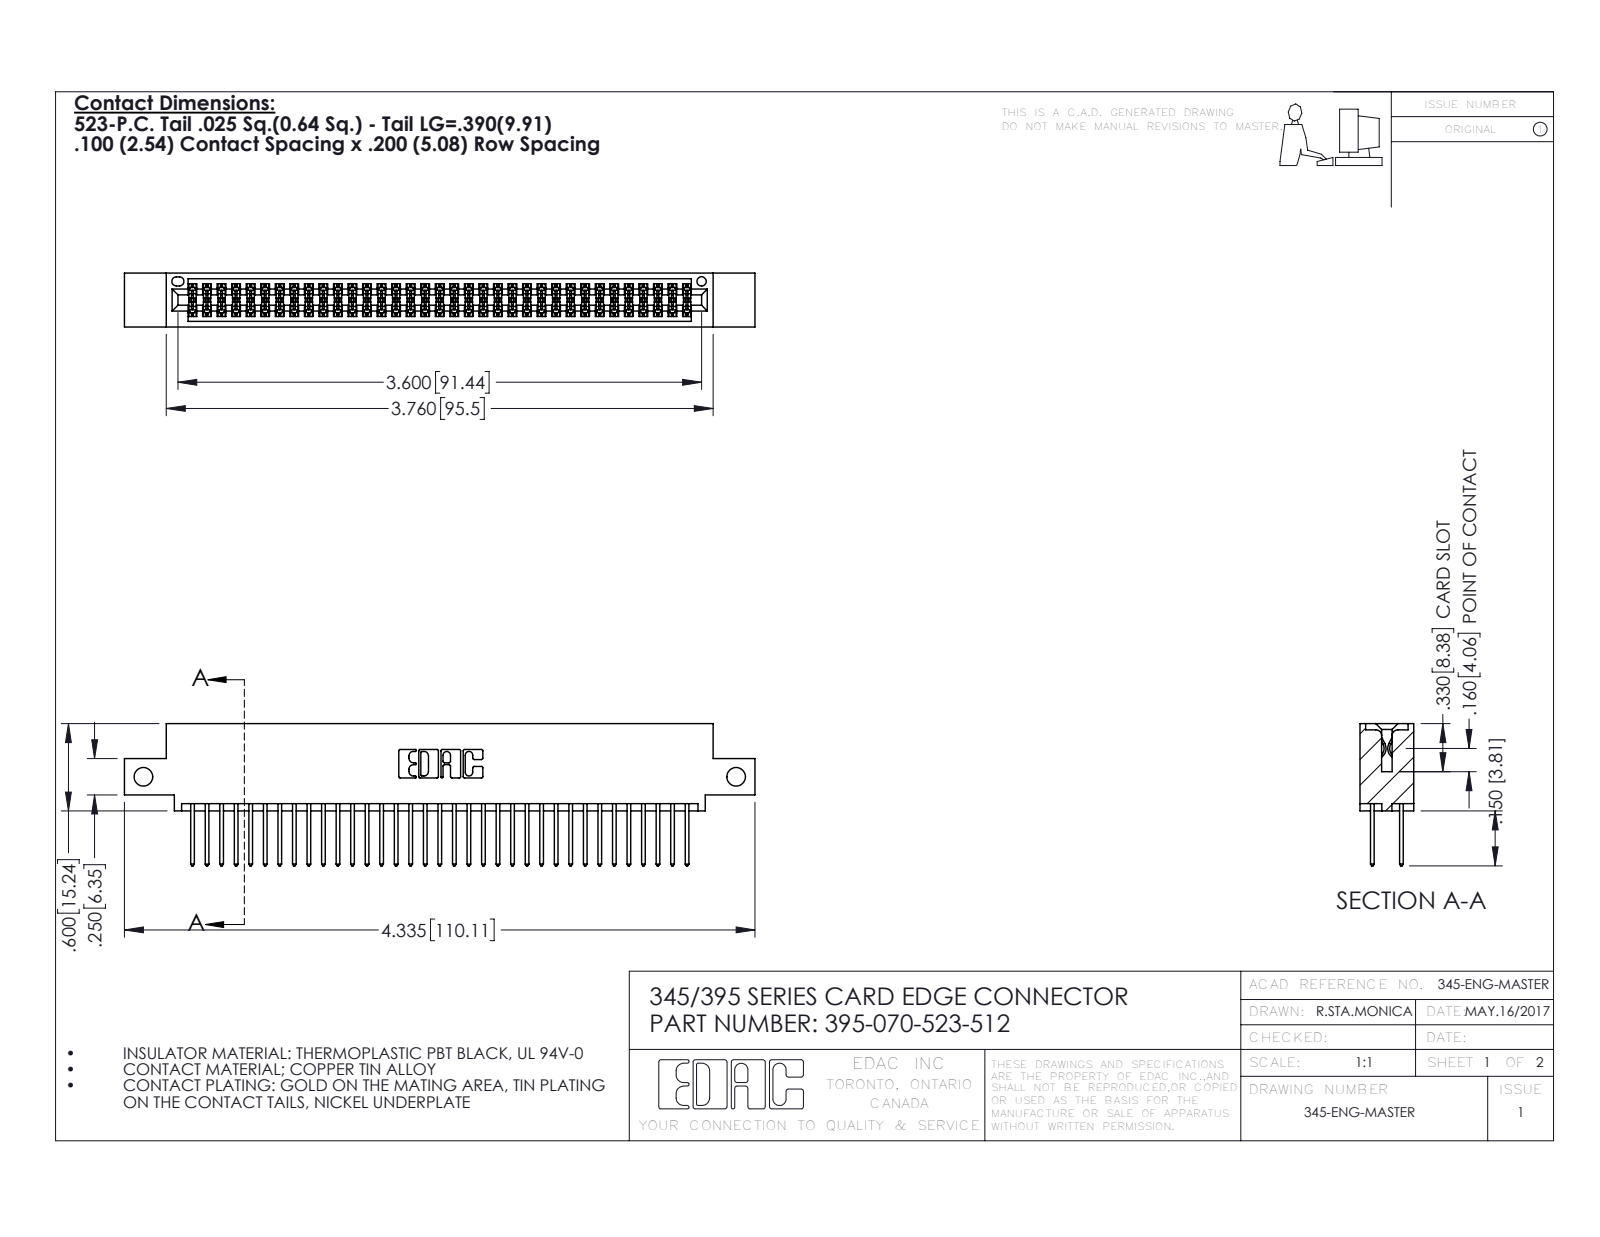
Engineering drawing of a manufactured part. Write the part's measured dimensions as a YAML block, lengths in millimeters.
part_name: "345-292-001_345-293-123; 345 Part_0.110 Offset - Side Mount; 395-070-523-512"
step_written_by: "SolidWorks 2016 (CONFIG_CONTROL_DESIGN)"
units: millimeters
bodies: {solids: 71, faces: 3630, planar: 2394, cylindrical: 1236, other: 0}
overall_size: [110.1, 24.8, 9.4]
volume: 10600
surface_area: 16150
round_holes:
  - {diameter: 3.3, count: 2}
  - {diameter: 1.6, count: 1}
partial_cylinders:
  - {radius: 0.2, count: 105}
  - {radius: 0.3, count: 70}
  - {radius: 0.3, count: 22}
  - {radius: 0.2, count: 6}
  - {radius: 0.8, count: 6}
  - {radius: 0.7, count: 3}
  - {radius: 0.4, count: 2}
  - {radius: 0.5, count: 2}
face_to_face_distances: [7.6, 1.8, 5.1, 2.5, 6.9, 0.6, 9.4, 5.7, 4.4, 3.8]
hole_center_spacings: [103.5]
